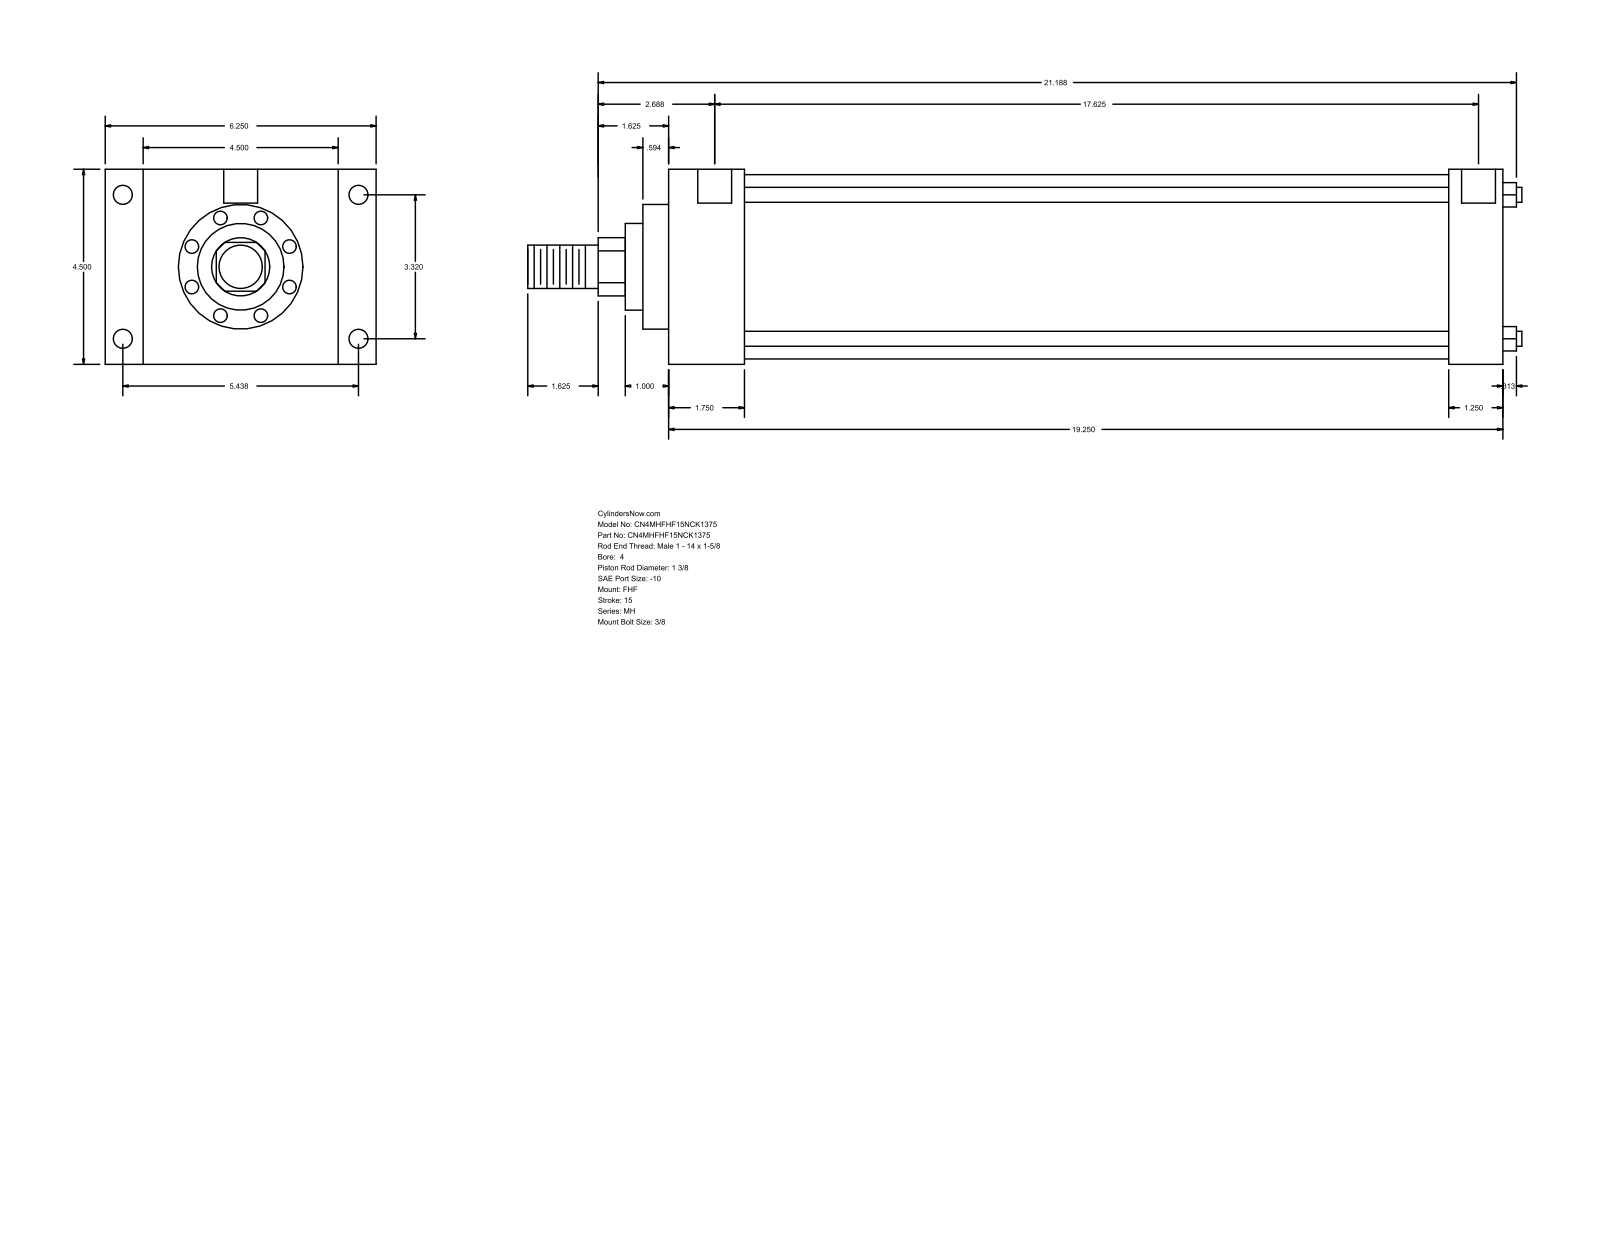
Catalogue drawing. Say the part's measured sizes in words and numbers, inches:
The part is named "MH_FHF__0400_1.375". Its 3-D file was written by "GSSL Pune (CONFIG_CONTROL_DESIGN)". It is 0 solids with 90 faces: 61 planar, 29 cylindrical and 0 other. Overall it measures 22.937 by 6.25 by 4.5 inches. Round holes: 4 of diameter 0.344, 4 of diameter 0.438, 2 of diameter 0.781. Round bosses or shafts: 4 of diameter 0.345, 1 of diameter 4.25, 1 of diameter 2.875, 1 of diameter 2, 1 of diameter 1.375, 1 of diameter 1. Partial cylindrical surfaces (rounded edges, fillets, slot ends): 1 of radius 0.672. The main face-to-face distances are 4.5, 19.25, 1.75, 17.5, 0.875, 5.375, 6.25, 18, 16.25, 1.25. The hole center spacings are 3.32, 5.438, 6.371, 17.75, 0.062, 0.063, 17.625, 17.687.
